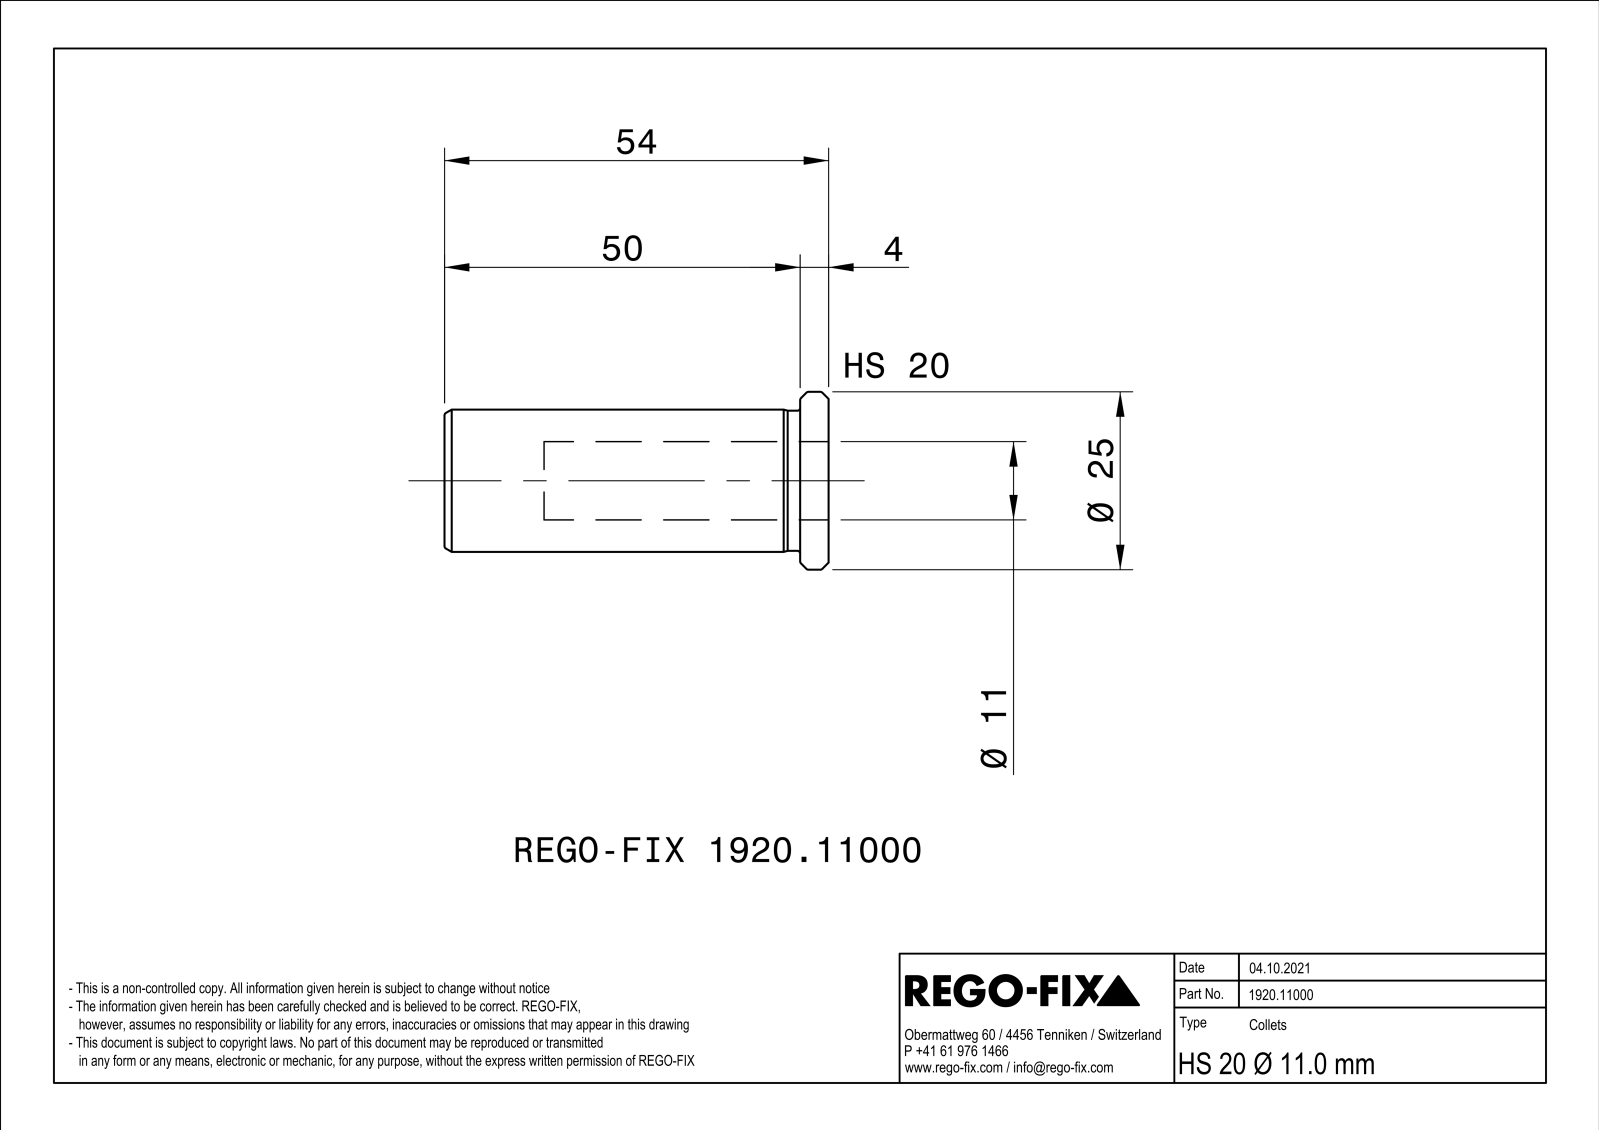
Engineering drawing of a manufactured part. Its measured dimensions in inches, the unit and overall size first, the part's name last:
Units: inches
Overall size (bounding box): 2.126 × 0.983 × 0.983
Round holes (diameter × count): ⌀0.433 ×1, ⌀0.65 ×1
Round bosses / shafts (diameter × count): ⌀0.984 ×1, ⌀0.787 ×1, ⌀0.776 ×1
Main face-to-face distances: 0.039, 0.157, 2.126, 1.969
Volume: 0.639 in³ · Surface area: 10.99 in²
Bodies: 1 solid, 71 faces (22 planar, 11 cylindrical, 38 other)
Part name (STEP PRODUCT): NOCUT
STEP written by: SIEMENS PLM Software Solid Edge ST10 (AUTOMOTIVE_DESIGN)
